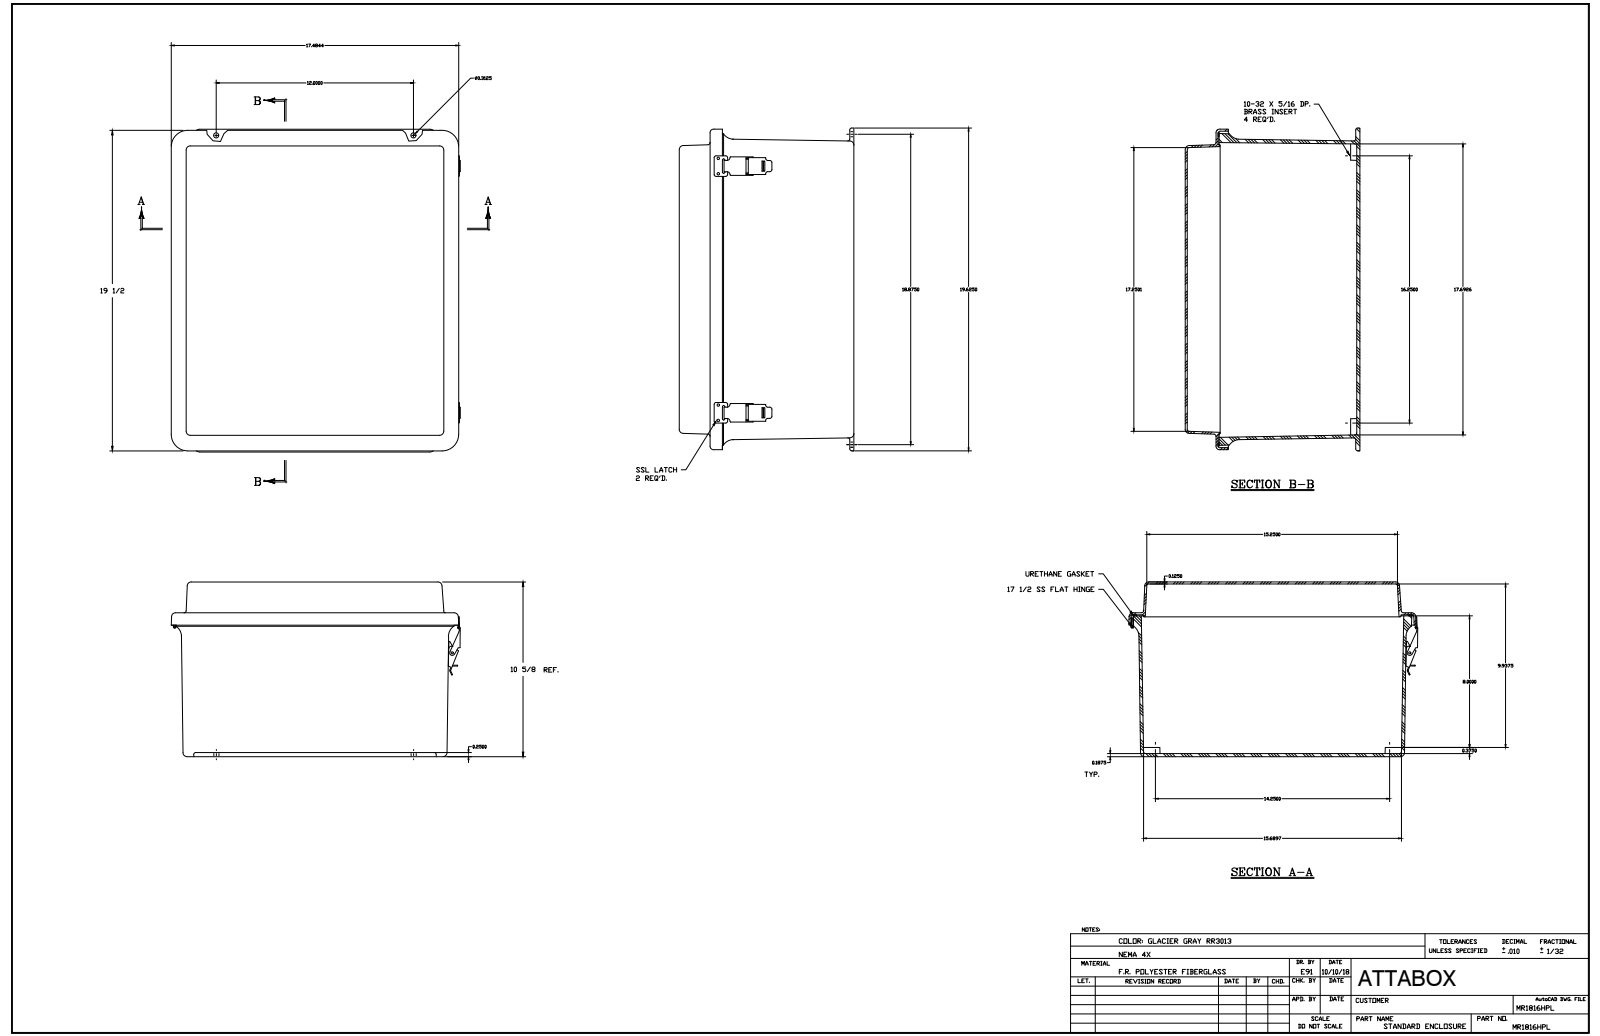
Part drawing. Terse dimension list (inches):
name: MR1816HPL
written by: SolidWorks 2018 (AUTOMOTIVE_DESIGN)
unit: in
bodies: 42 solids, 1200 faces (530 planar, 495 cylindrical, 175 other)
size: 19.625 × 17.629 × 10.642
volume: 249.6 in³; area: 2 949 in²
holes: 24× ⌀0.14, 12× ⌀0.131, 8× ⌀0.104, 5× ⌀0.152, 4× ⌀0.13, 4× ⌀0.156, 4× ⌀0.218, 2× ⌀0.135, 2× ⌀0.375, 1× ⌀0.085, 1× ⌀0.135
bosses: 12× ⌀0.25, 12× ⌀0.125, 8× ⌀0.125, 4× ⌀0.27, 1× ⌀0.3, 1× ⌀0.17, 1× ⌀0.155, 1× ⌀0.155
rounds: 28× R0.125, 20× R0.015, 20× R0.031, 16× R0.045, 12× R0.03, 12× R0.25, 8× R0.023, 6× R0.06
face distances: 0.187, 0.188, 0.125, 10.517, 10.329, 10.642, 10.454, 2, 0.125, 8.642
hole spacings: 3.375, 3.375, 6.75, 0.25, 10.25, 14.984, 9.75, 10
